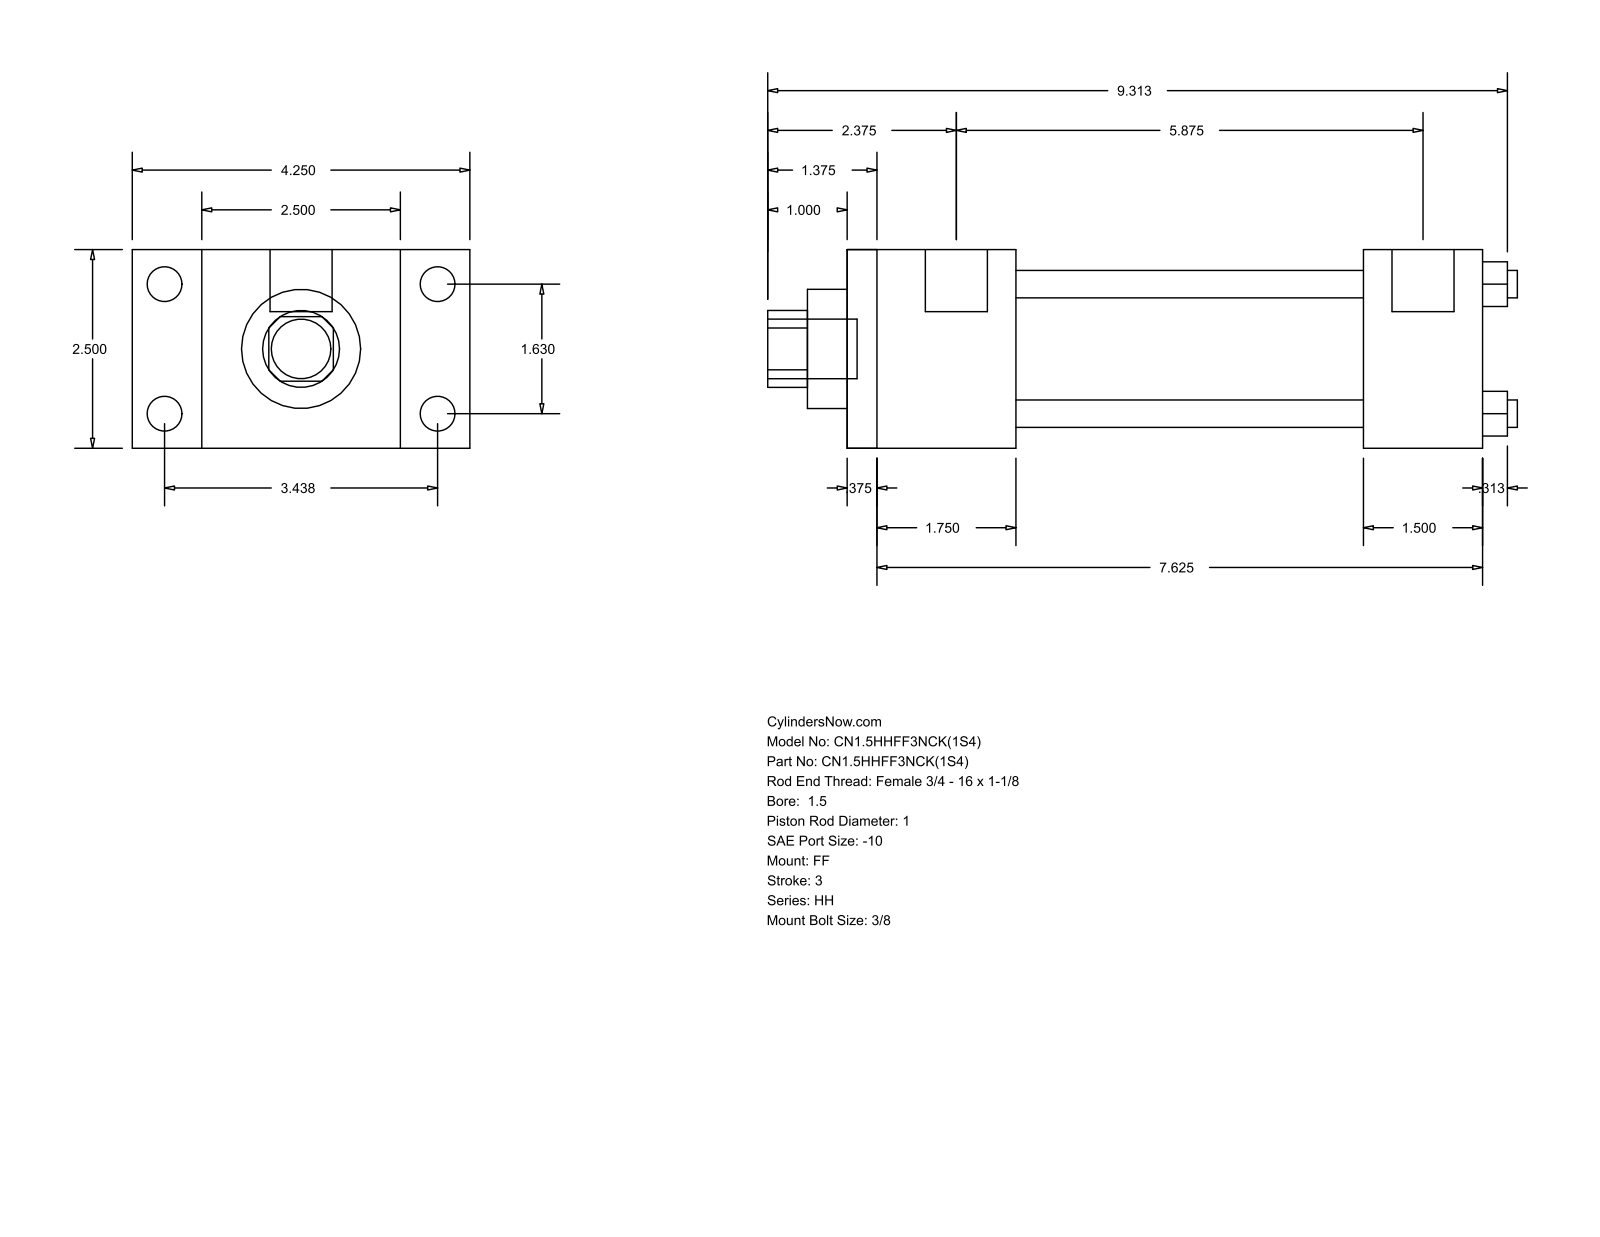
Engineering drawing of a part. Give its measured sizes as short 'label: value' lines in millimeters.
name: HH_FF__0150_1
written by: GSSL Pune (CONFIG_CONTROL_DESIGN)
unit: mm
bodies: 0 solids, 92 faces (64 planar, 28 cylindrical, 0 other)
size: 239.71 × 107.95 × 63.5
holes: 4× ⌀8.76, 1× ⌀25.4, 1× ⌀38.1, 1× ⌀44.45
bosses: 4× ⌀11.13, 4× ⌀5.56, 2× ⌀19.84, 1× ⌀19.05
rounds: 1× R12.29
face distances: 63.5, 203.2, 9.52, 193.68, 53.98, 44.46, 149.22, 165.1, 155.58, 111.12
hole spacings: 29.27, 41.4, 58.55
